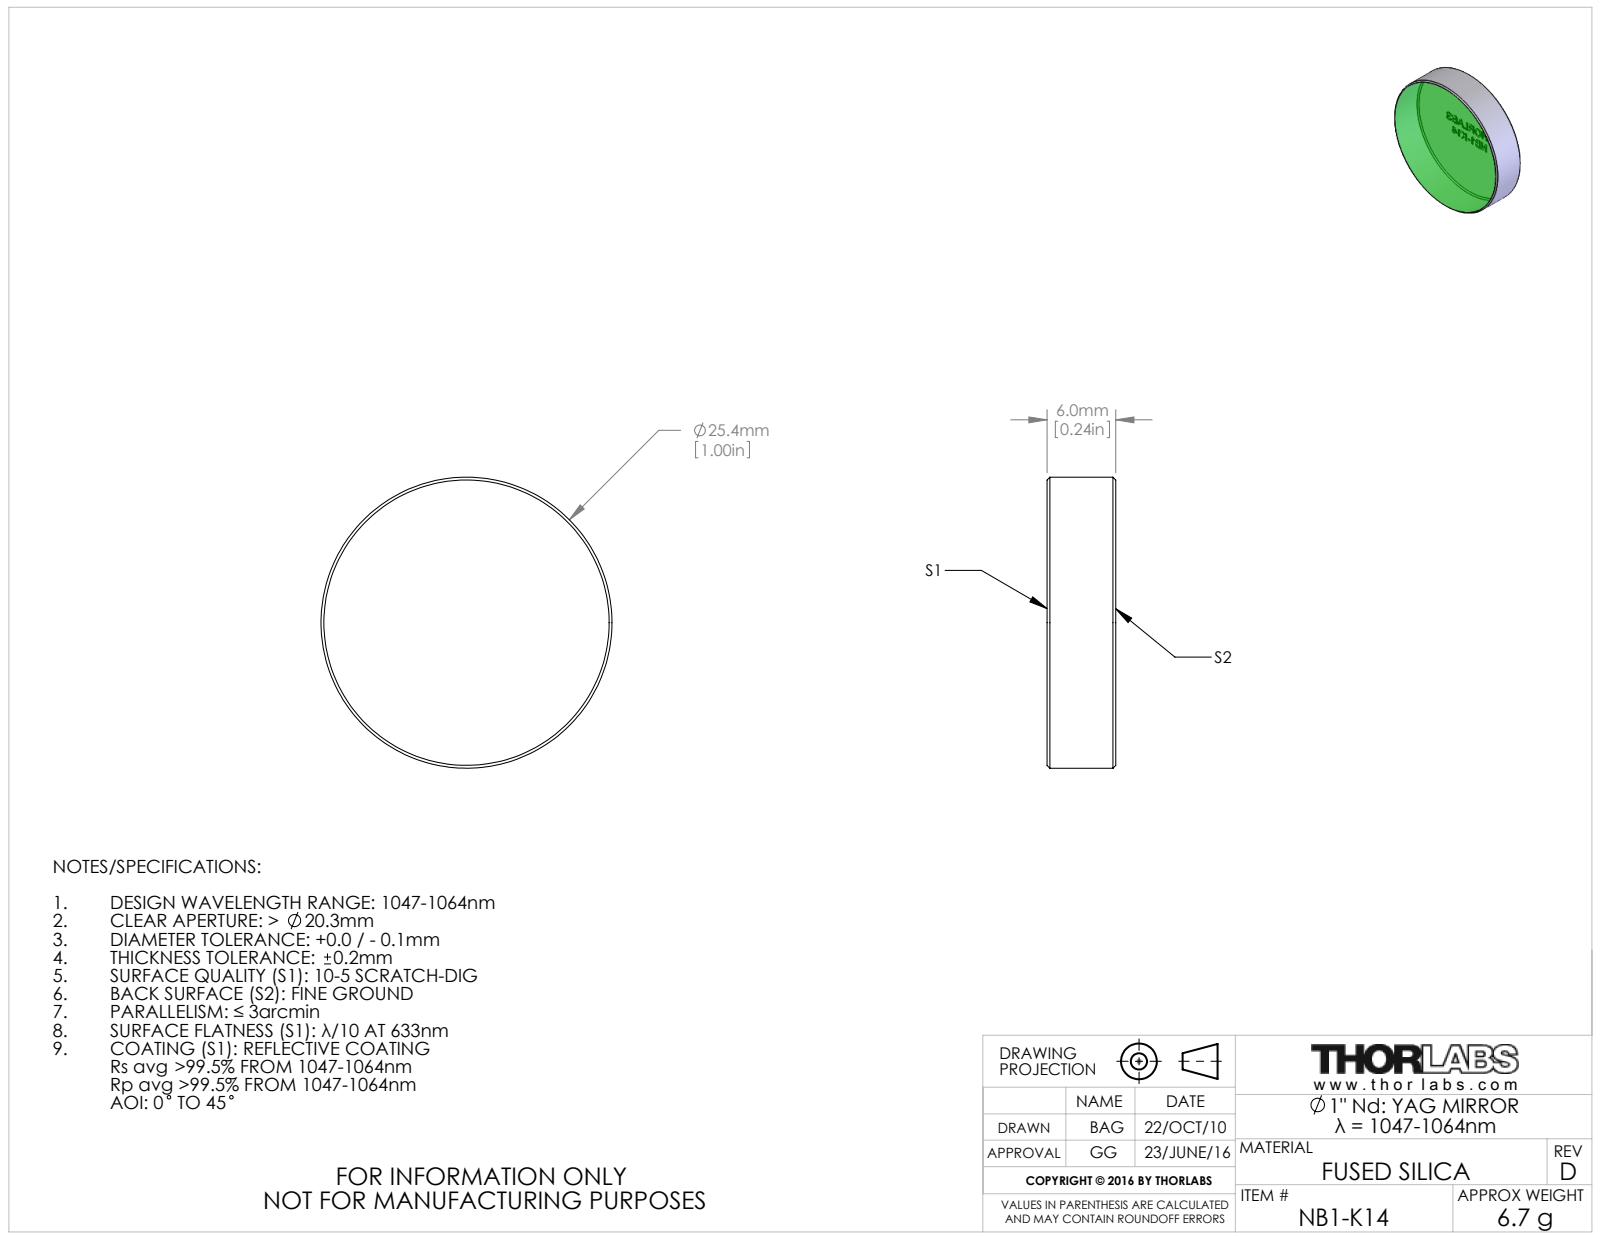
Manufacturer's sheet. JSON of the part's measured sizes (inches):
{"part_name": "19192-E0W", "step_written_by": "SolidWorks 2016 (CONFIG_CONTROL_DESIGN)", "units": "inches", "bodies": {"solids": 1, "faces": 205, "planar": 143, "cylindrical": 2, "other": 60}, "overall_size": [1, 1, 0.236], "volume_in3": 0.185, "surface_area_in2": 2.276, "round_bosses_or_shafts": [[1, 1]], "face_to_face_distances": [0.236, 0.061, 0.131, 0.093, 0.094, 0.076, 0.086, 0.038, 0.058, 0.14]}
